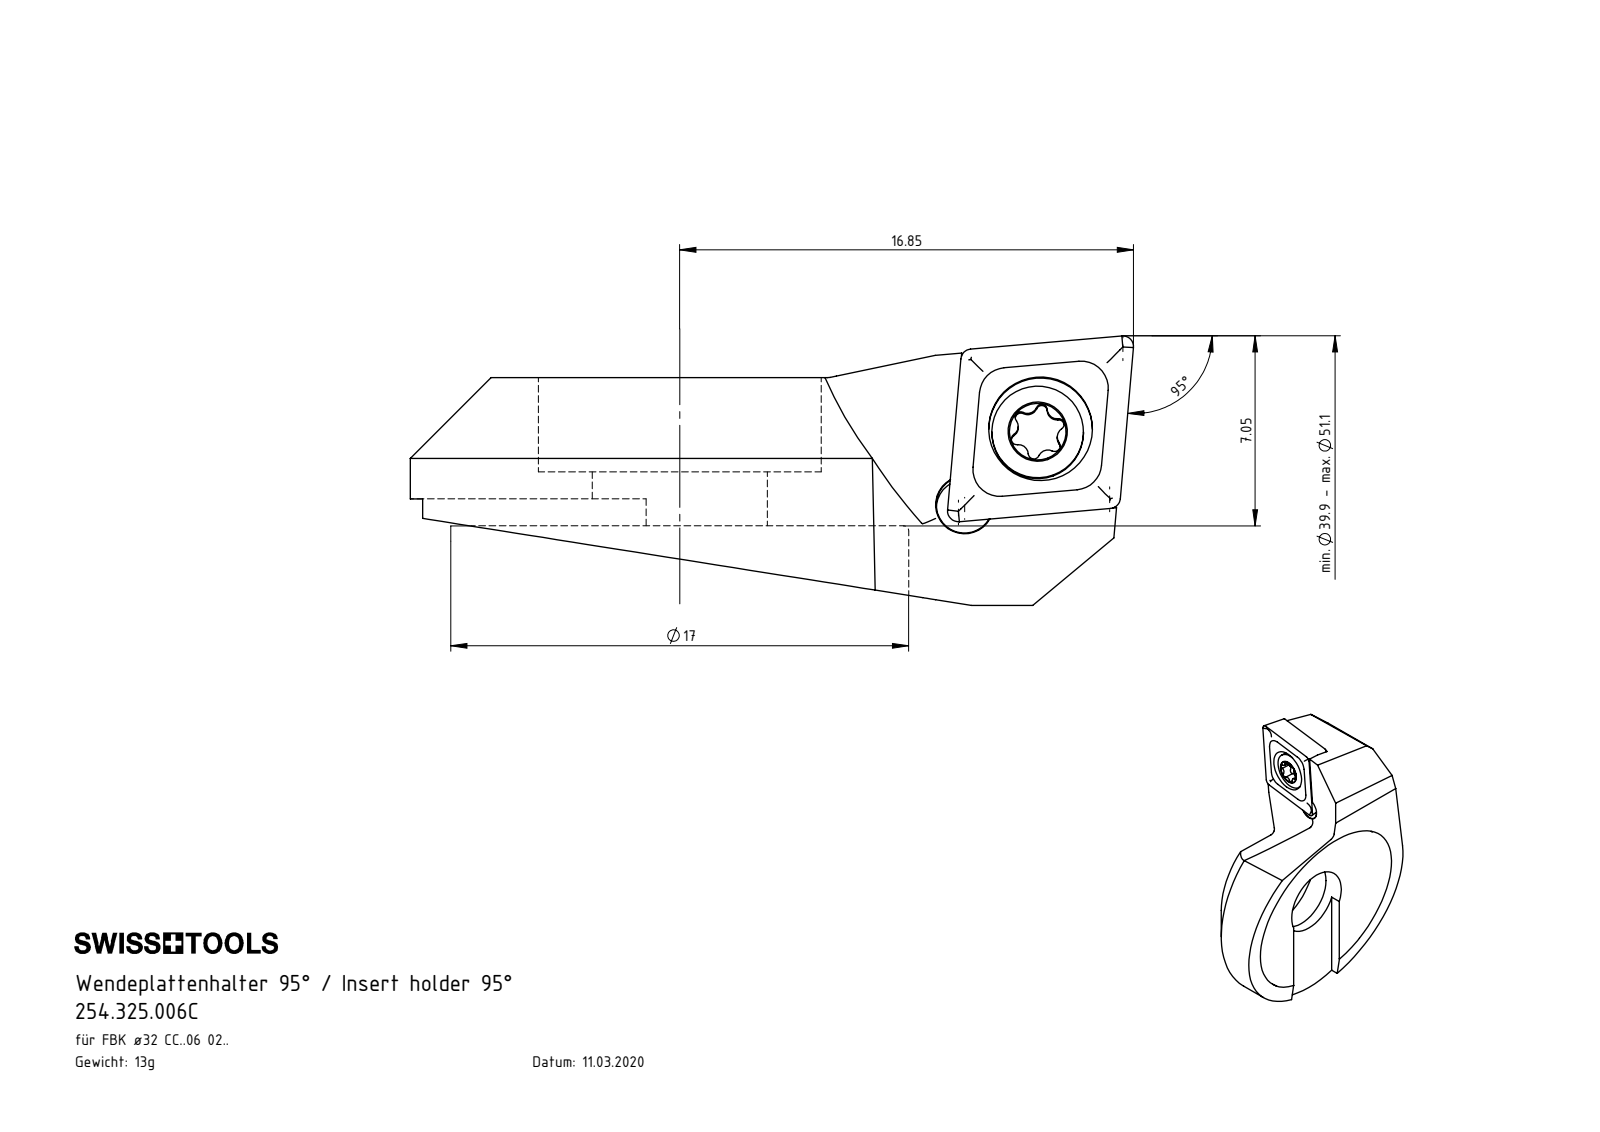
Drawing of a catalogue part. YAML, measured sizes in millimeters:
part_name: "CCMT060204; F32-WCA.002.007_A_fertigbearbeitet; 254.325.006C; WCA-ER2.001.006_A"
step_written_by: "SolidWorks 2017 (CONFIG_CONTROL_DESIGN)"
units: millimeters
bodies: {solids: 3, faces: 135, planar: 40, cylindrical: 45, other: 50}
overall_size: [26.85, 20, 10]
volume: 1584
surface_area: 1546
round_holes:
  - {diameter: 2, count: 1}
  - {diameter: 2.05, count: 1}
  - {diameter: 2.8, count: 1}
  - {diameter: 3.85, count: 1}
  - {diameter: 6.5, count: 1}
  - {diameter: 10.5, count: 1}
round_bosses_or_shafts:
  - {diameter: 3.4, count: 1}
  - {diameter: 2.5, count: 1}
partial_cylinders:
  - {radius: 0.21, count: 6}
  - {radius: 0.36, count: 5}
  - {radius: 1, count: 4}
  - {radius: 0.36, count: 1}
  - {radius: 4, count: 1}
  - {radius: 8.5, count: 1}
  - {radius: 10, count: 1}
  - {radius: 12, count: 1}
face_to_face_distances: [1, 2, 4.95, 3.95, 2.95, 2.28, 2.38, 6, 2.68, 2.58]
hole_center_spacings: [3.91, 4.01]
